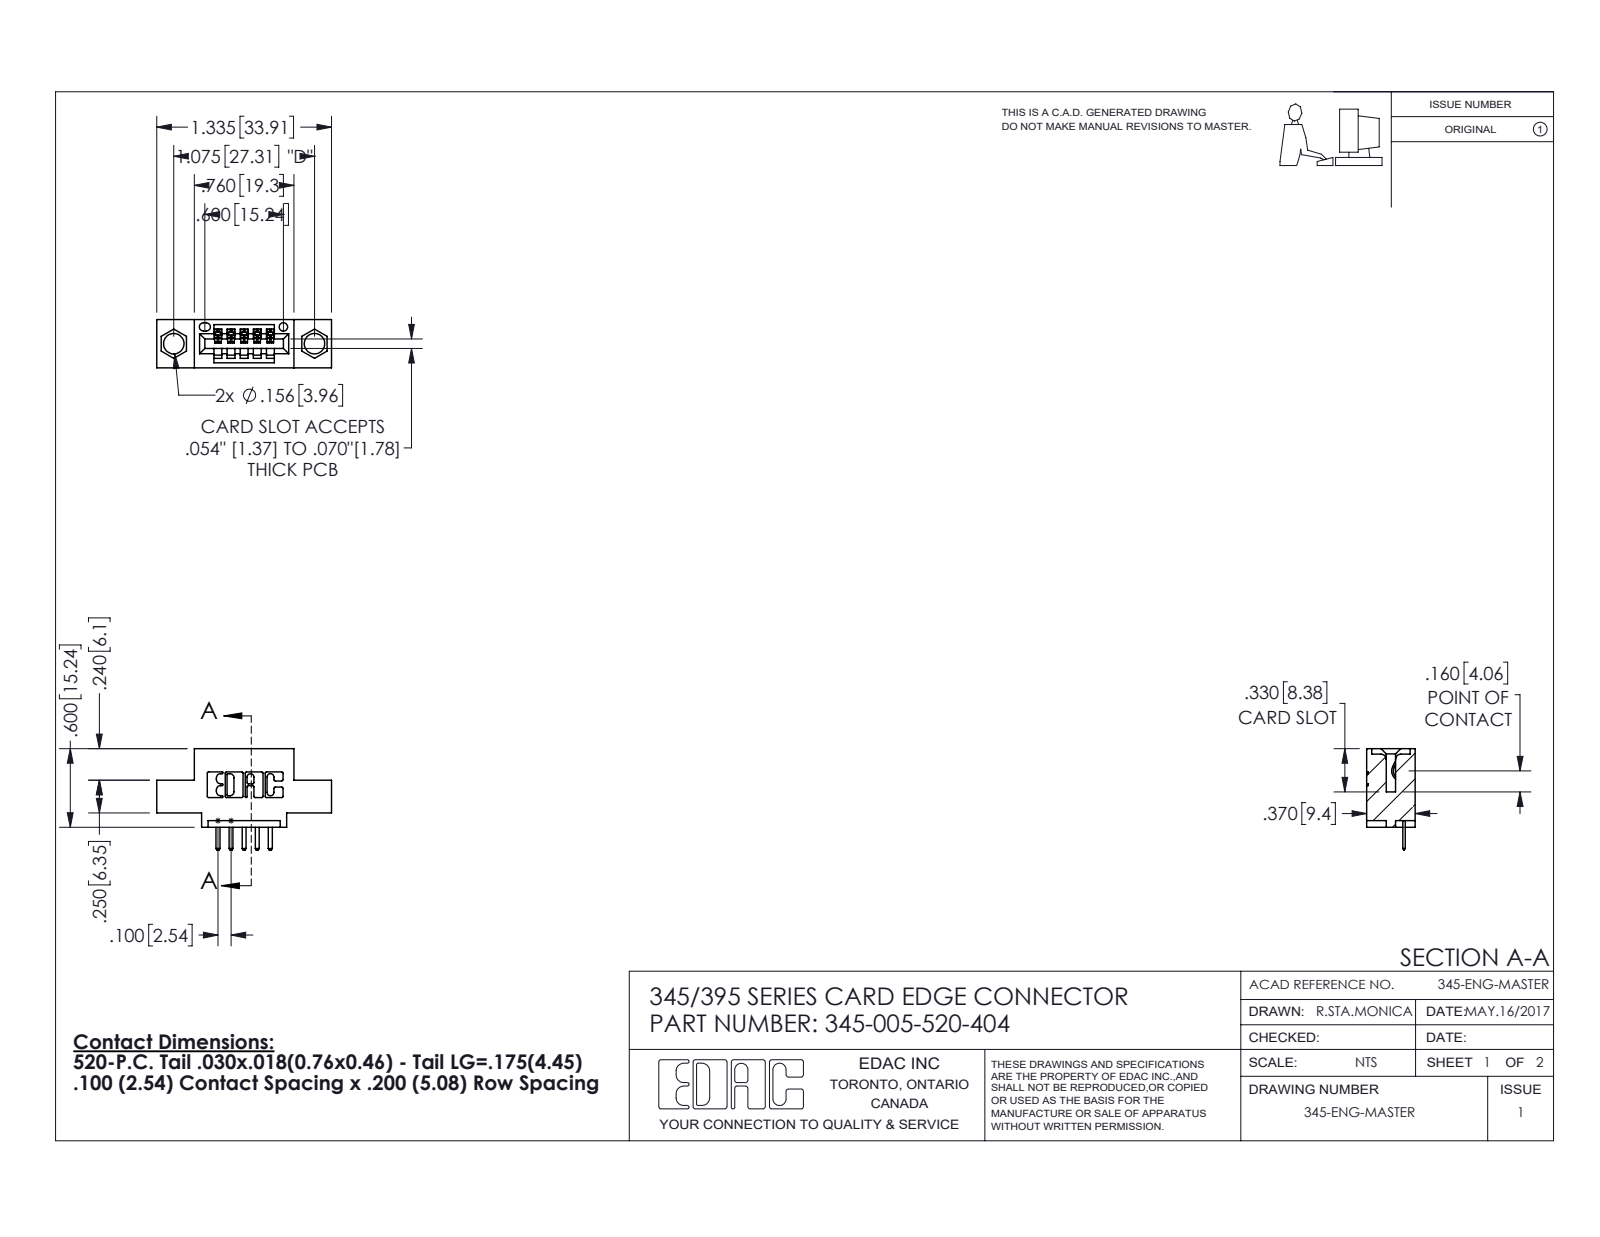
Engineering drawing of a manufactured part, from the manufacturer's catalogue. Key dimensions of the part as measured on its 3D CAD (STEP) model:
Part name (STEP PRODUCT): 345-292-001_345-293-120; 345 Part_0.110 Offset - 0.156 Dia-TH; 345-005-520-404
STEP written by: SolidWorks 2016 (CONFIG_CONTROL_DESIGN)
Units: inches
Bodies: 6 solids, 440 faces (294 planar, 146 cylindrical, 0 other)
Overall size (bounding box): 1.335 × 0.775 × 0.37
Volume: 0.167 in³ · Surface area: 4.626 in²
Round holes (diameter × count): ⌀0.156 ×2, ⌀0.064 ×1
Partial cylindrical surfaces — rounded edges, fillets, slot ends (radius × count): R0.01 ×22, R0.01 ×12, R0.006 ×10, R0.007 ×6, R0.031 ×6, R0.026 ×3, R0.031 ×2, R0.04 ×2
Main face-to-face distances: 0.37, 0.2, 0.1, 0.298, 0.072, 0.25, 0.025, 0.06, 0.16, 0.55
Hole centre spacings: 0.27, 0.847, 1.075
